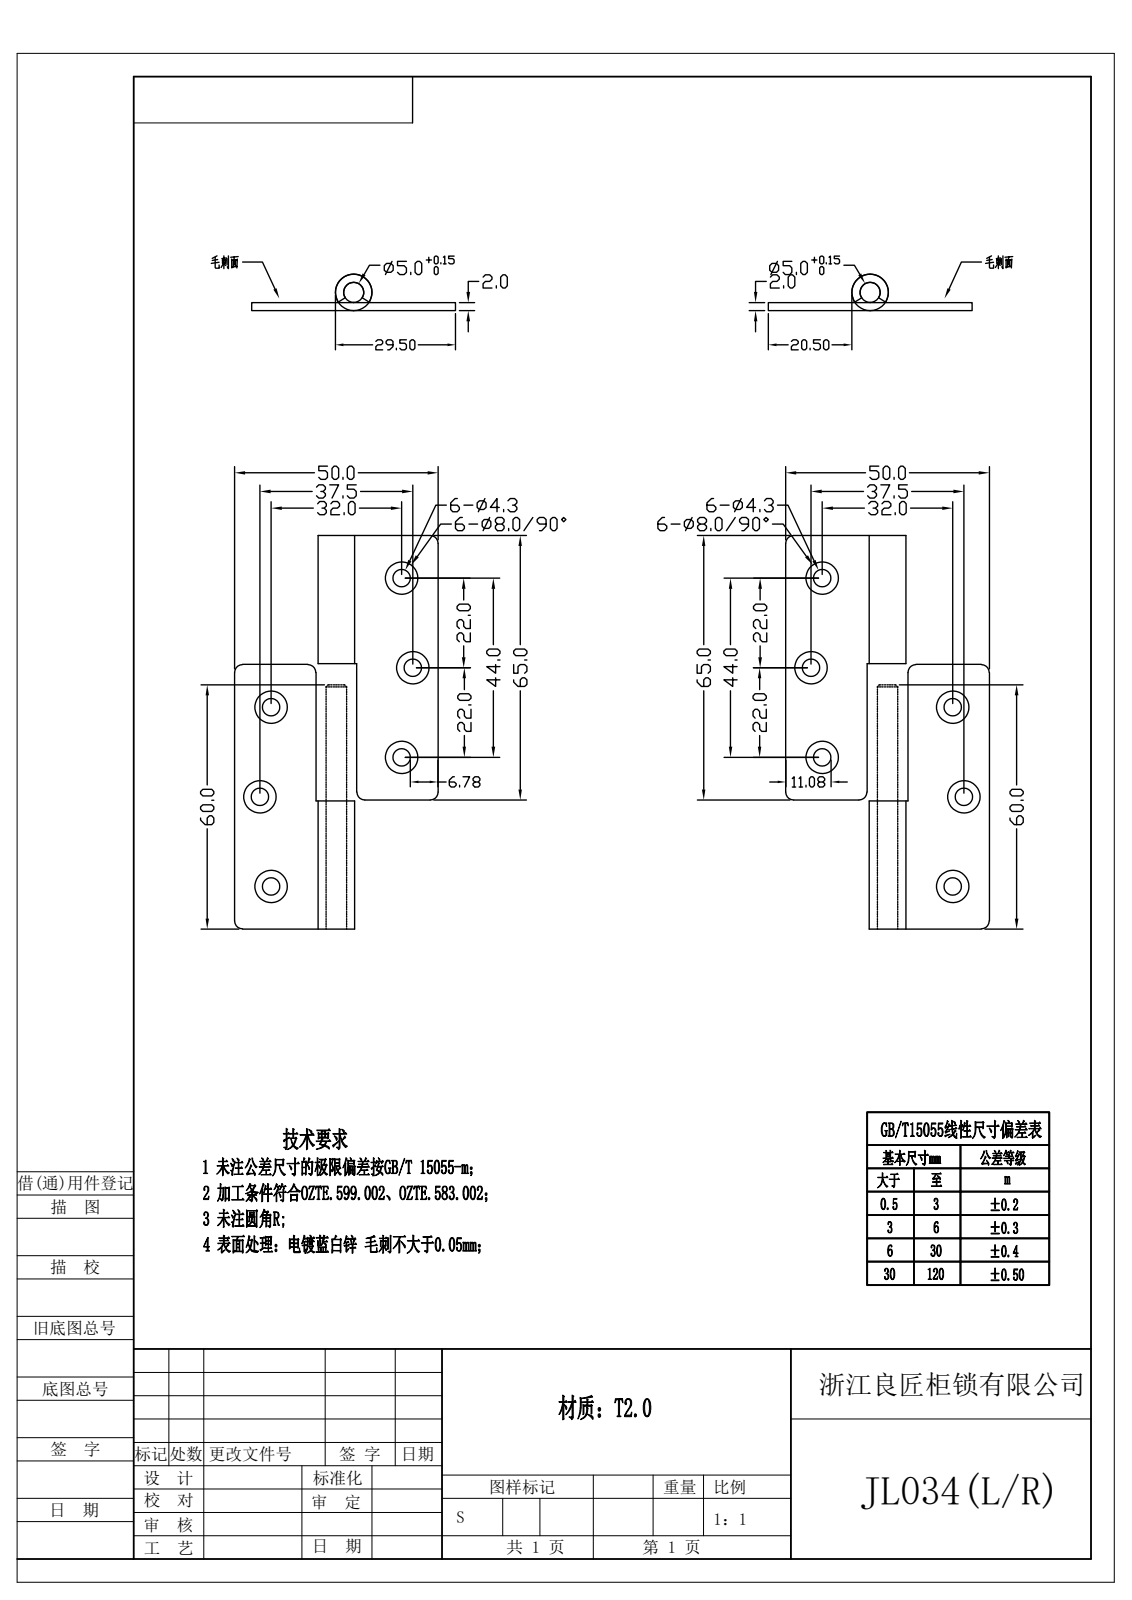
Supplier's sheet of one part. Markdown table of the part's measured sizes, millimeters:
| quantity | value |
| --- | --- |
| STEP written by | Rhino 8.5 (CONFIG_CONTROL_DESIGN) |
| units | millimeters |
| bodies | 8 solids, 165 faces (93 planar, 35 cylindrical, 37 other) |
| overall size | 120.11 × 94.57 × 11.19 |
| volume | 17 968 mm³ |
| surface area | 20 461 mm² |
| round holes (diameter × count) | 5 × 2 |
| round bosses / shafts (diameter × count) | 9 × 2 |
| partial cylindrical surfaces (radius × count) | 2 × 12, 49.94 × 1, 65.67 × 1, 80.31 × 1 |
| main face-to-face distances | 2, 4, 70.11, 0.93, 20, 30, 50, 65, 31.5, 33.5 |
| hole center spacings | 70.14 |
